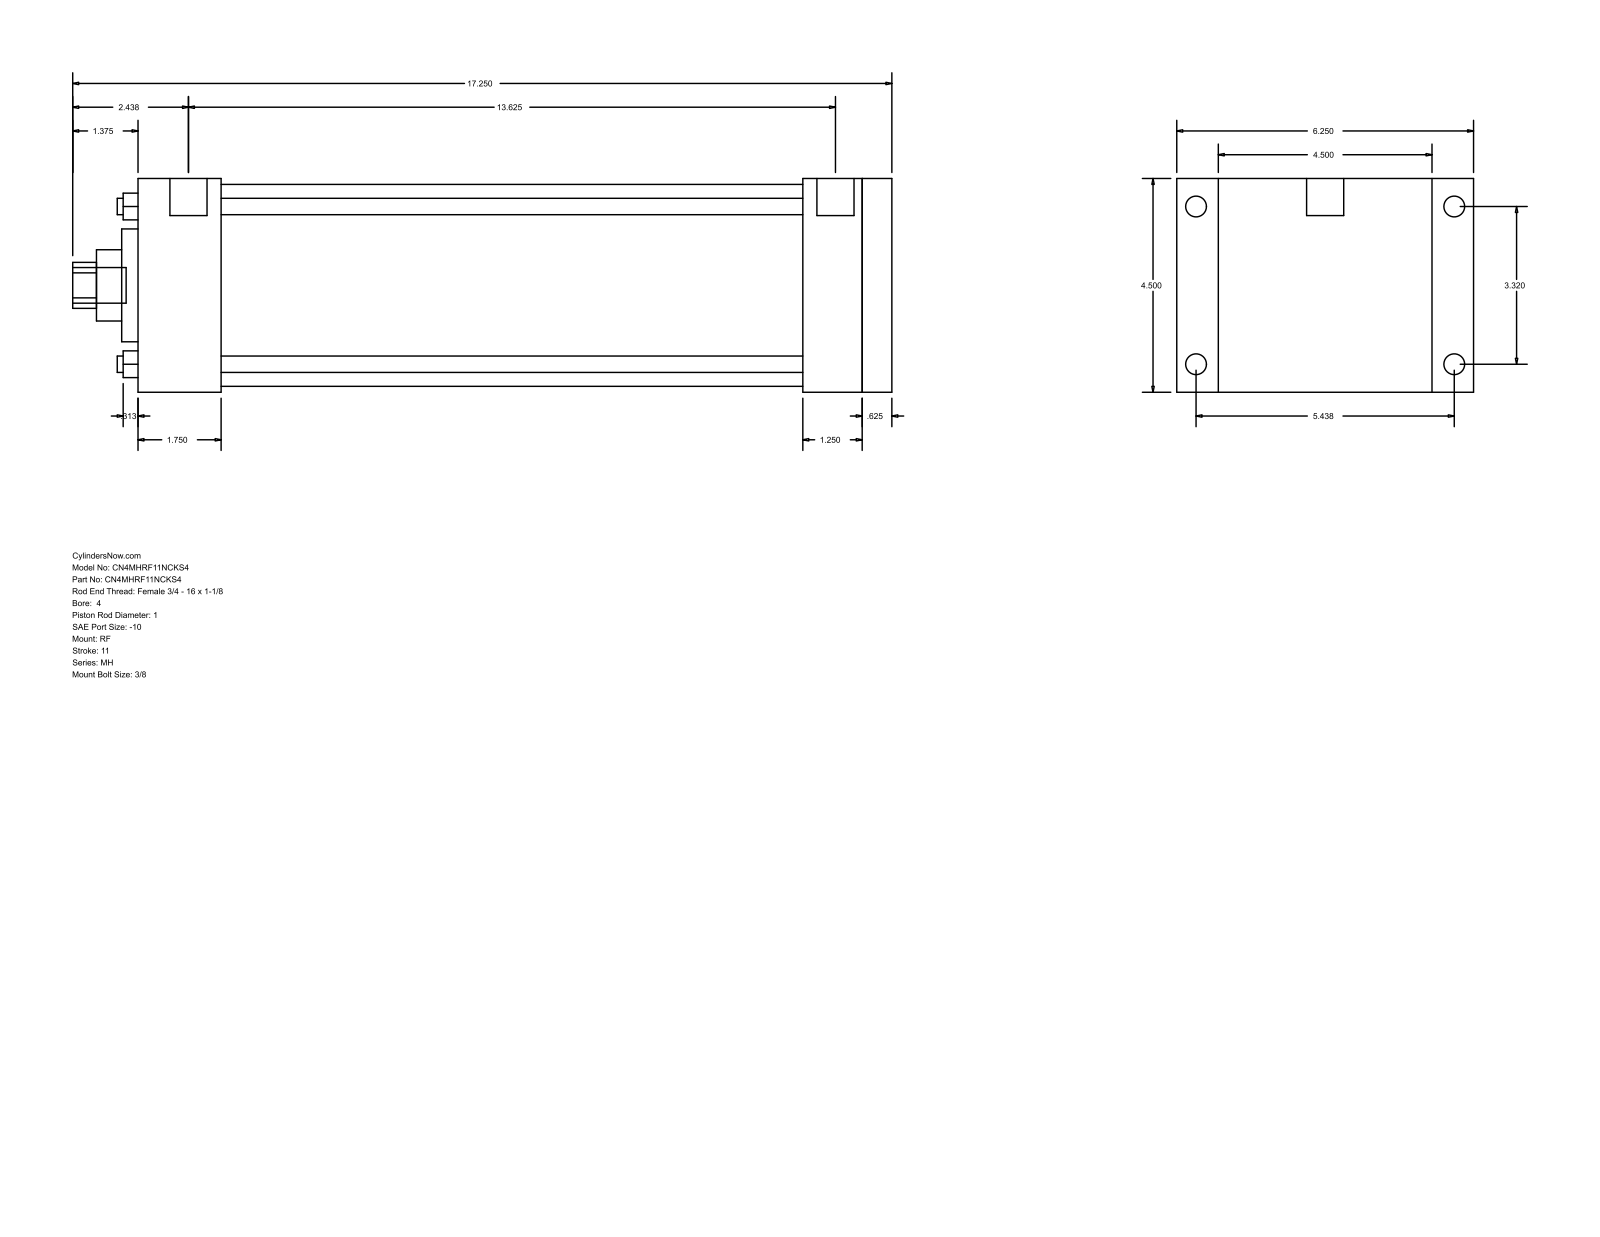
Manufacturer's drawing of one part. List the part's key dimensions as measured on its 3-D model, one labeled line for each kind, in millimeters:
Part name (STEP PRODUCT): MH_RF__0400_1
STEP written by: GSSL Pune (CONFIG_CONTROL_DESIGN)
Units: millimetres
Bodies: 0 solids, 94 faces (65 planar, 29 cylindrical, 0 other)
Overall size (bounding box): 438.15 × 158.75 × 114.3
Round holes (diameter × count): ⌀8.76 ×4, ⌀25.4 ×1, ⌀38.1 ×1, ⌀60.33 ×1, ⌀107.95 ×1
Round bosses / shafts (diameter × count): ⌀11.13 ×4, ⌀8.73 ×4, ⌀19.84 ×2, ⌀19.05 ×1
Partial cylindrical surfaces — rounded edges, fillets, slot ends (radius × count): R12.29 ×1
Main face-to-face distances: 114.3, 403.23, 387.35, 15.88, 47.63, 44.46, 342.89, 358.77, 355.6, 311.14
Hole centre spacings: 59.62, 84.32, 119.25
